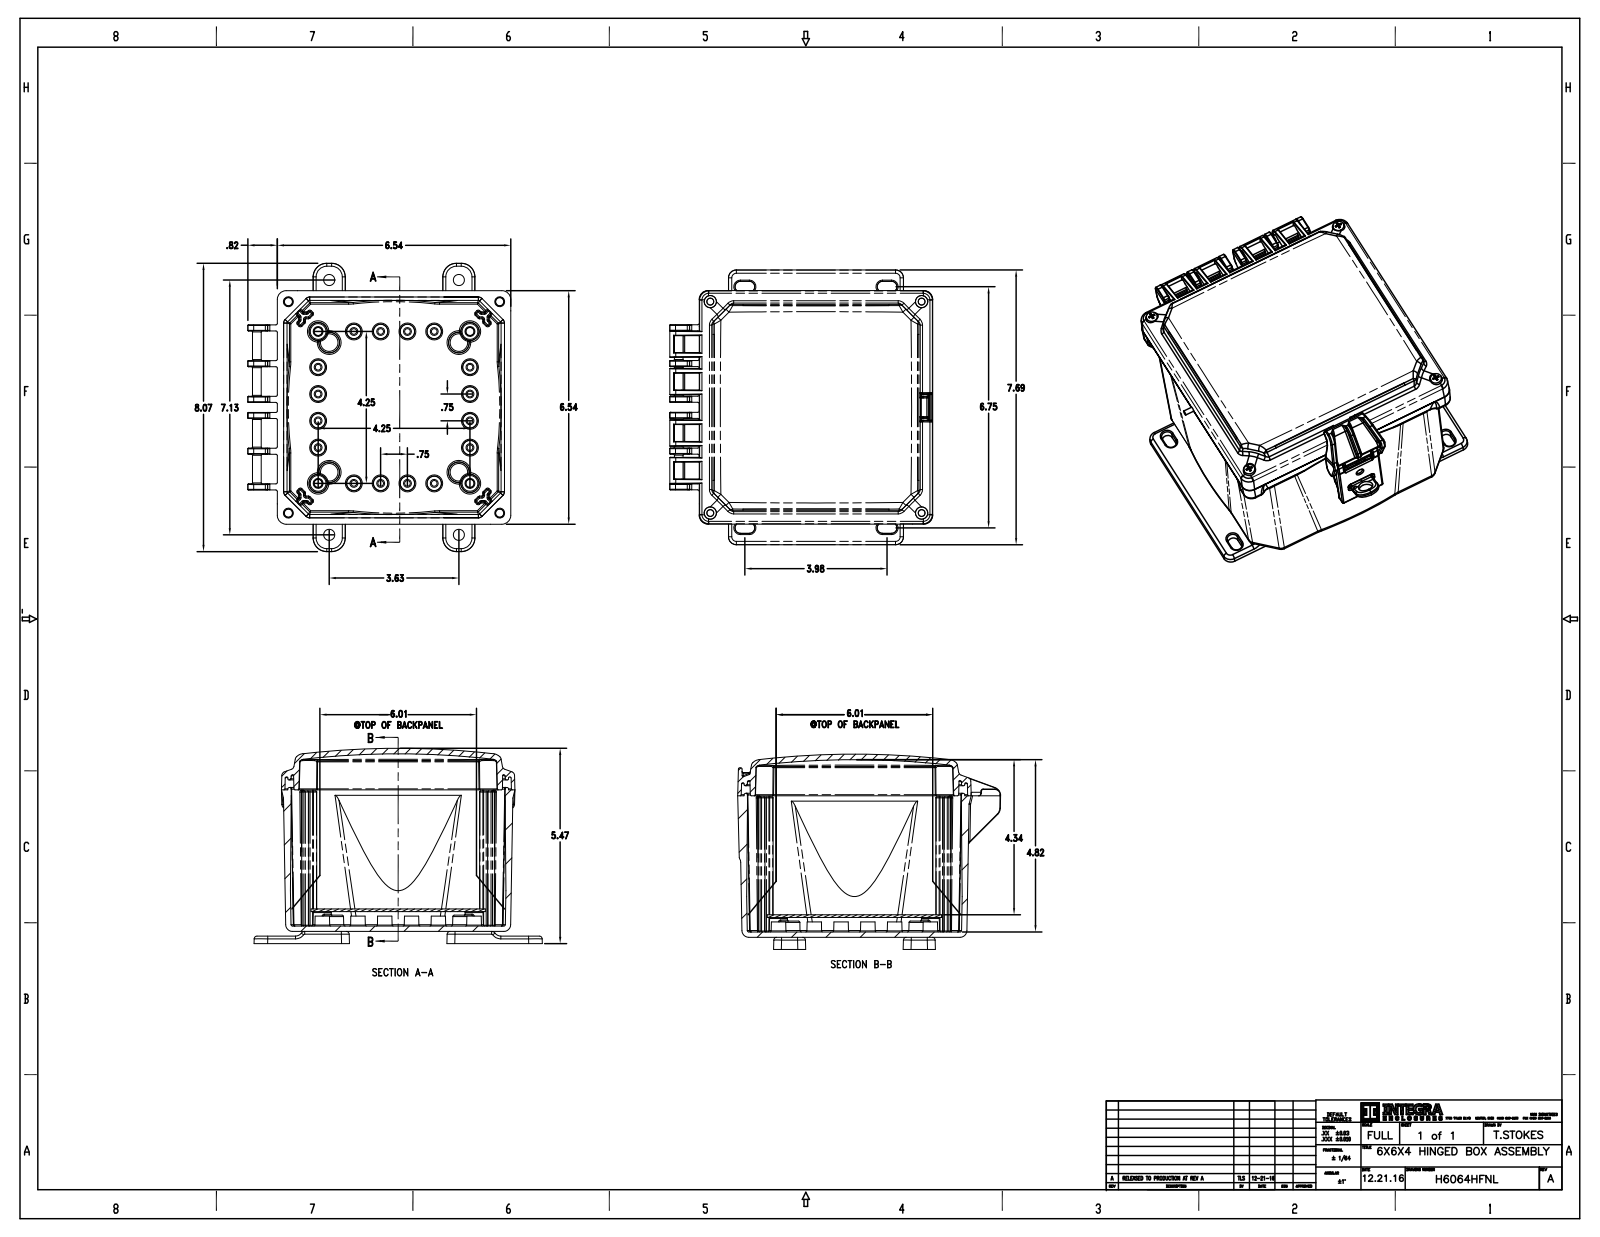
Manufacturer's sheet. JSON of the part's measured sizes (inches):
{"part_name": "H664BH; 9912525-80-10; 9912521-80-10; H664BH_ASM (+5 more)", "step_written_by": "CREO PARAMETRIC BY PTC INC, 2016050 (CONFIG_CONTROL_DESIGN)", "units": "inches", "bodies": {"solids": 24, "faces": 3845, "planar": 895, "cylindrical": 1536, "other": 1414}, "overall_size": [7.69, 7.359, 5.465], "volume_in3": 39.56, "surface_area_in2": 552, "round_holes": [[0.16, 16], [0.19, 8], [0.201, 4]], "round_bosses_or_shafts": [[0.25, 12], [0.3, 8], [0.298, 8], [0.29, 8], [0.26, 8], [0.258, 8], [0.375, 4], [0.372, 4]], "partial_cylinders_radius": [[0.03, 349], [0.02, 89], [0.015, 60], [0.025, 60], [0.005, 48], [0.04, 37], [0.09, 36], [0.1, 28]], "face_to_face_distances": [0.15, 0.49, 3.81, 0.12, 0.34, 3.96, 0.392, 0.22, 4.3, 5.694], "hole_center_spacings": [4.25, 4.315, 4.596, 0.75, 0.757, 1, 1.473, 1.5]}
